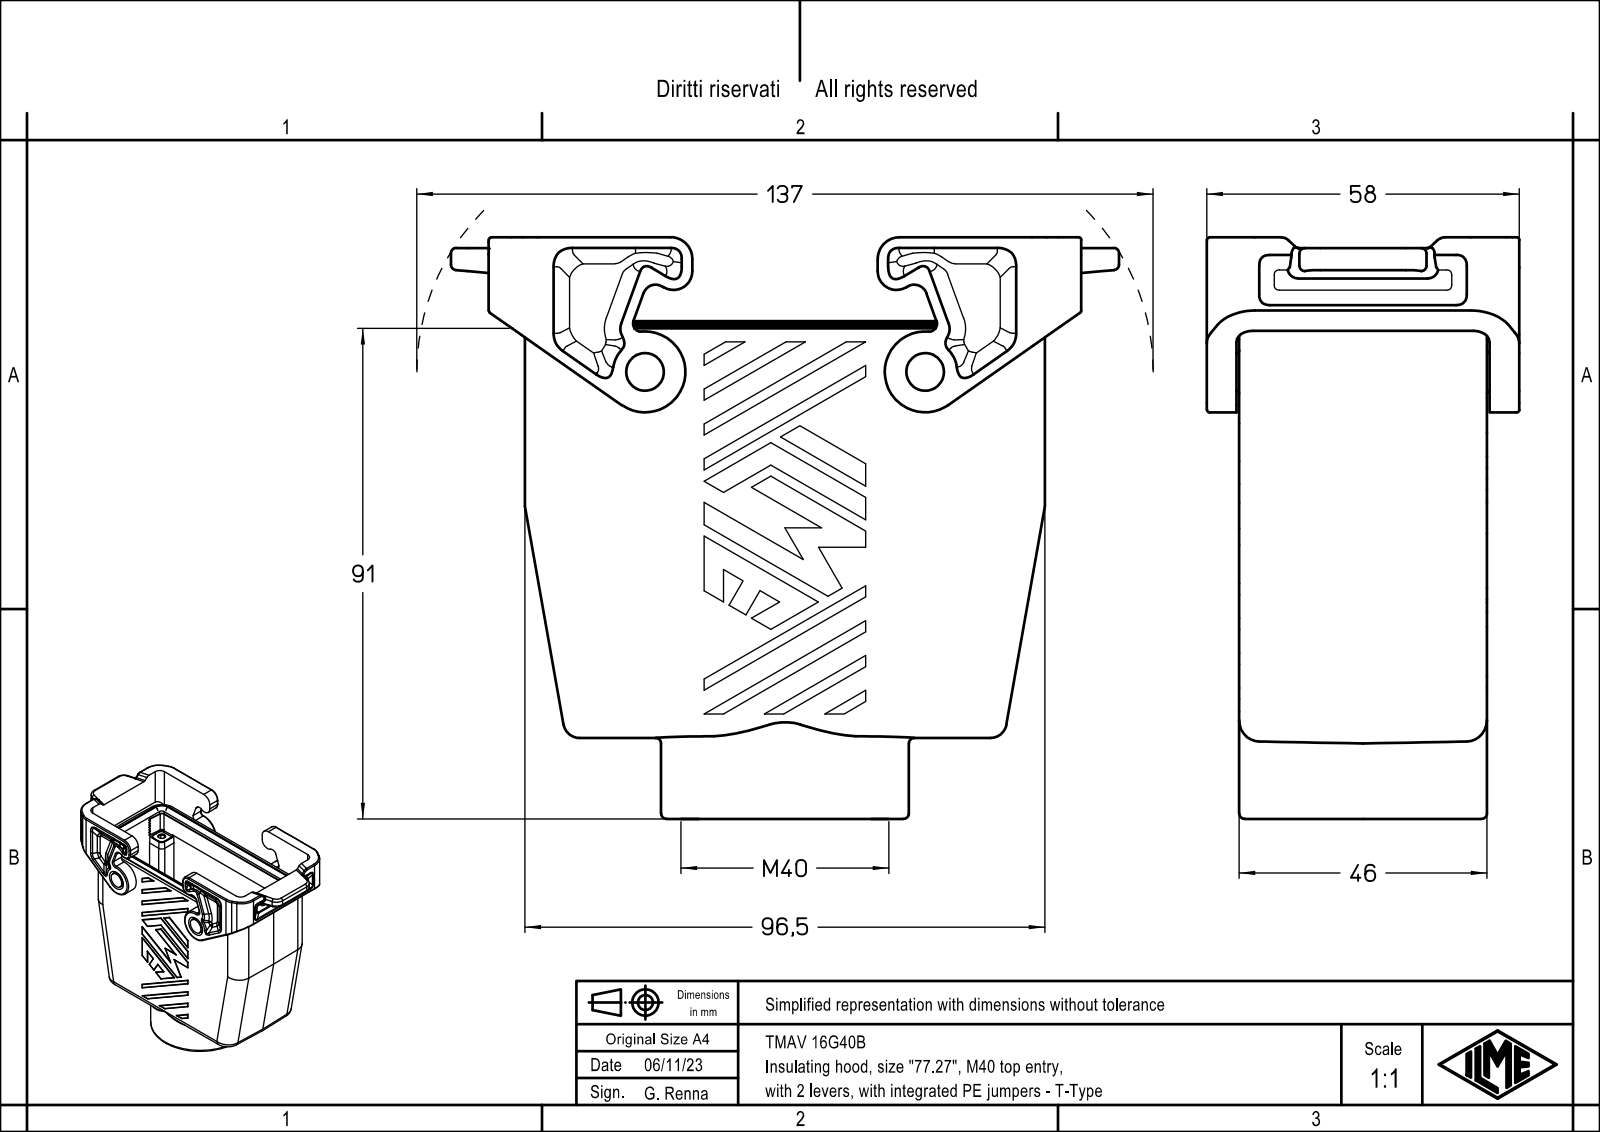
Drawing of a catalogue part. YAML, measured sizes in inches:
part_name: "TMAV 16G40B"
step_written_by: "Creo Elements/Direct Modeling 20.1B 02-Apr-2019 (C) Parametric Technology GmbH (AUTOMOTIVE_DESIGN)"
units: inches
bodies: {solids: 1, faces: 754, planar: 374, cylindrical: 318, other: 62}
overall_size: [4.882, 4.248, 2.283]
volume: 9.369
surface_area: 99.97
round_holes:
  - {diameter: 0.138, count: 4}
  - {diameter: 1.339, count: 1}
  - {diameter: 1.52, count: 1}
round_bosses_or_shafts:
  - {diameter: 0.276, count: 2}
  - {diameter: 1.811, count: 1}
partial_cylinders:
  - {radius: 0.006, count: 88}
  - {radius: 0.079, count: 20}
  - {radius: 0.118, count: 20}
  - {radius: 0.059, count: 18}
  - {radius: 0.039, count: 16}
  - {radius: 0.051, count: 12}
  - {radius: 0.236, count: 8}
  - {radius: 0.276, count: 8}
face_to_face_distances: [0.213, 1.598, 1.386, 1.811, 0.02, 0.232, 1.618, 1.831, 0.217, 0.236]
hole_center_spacings: [1.615, 1.063, 3.051, 3.231]
